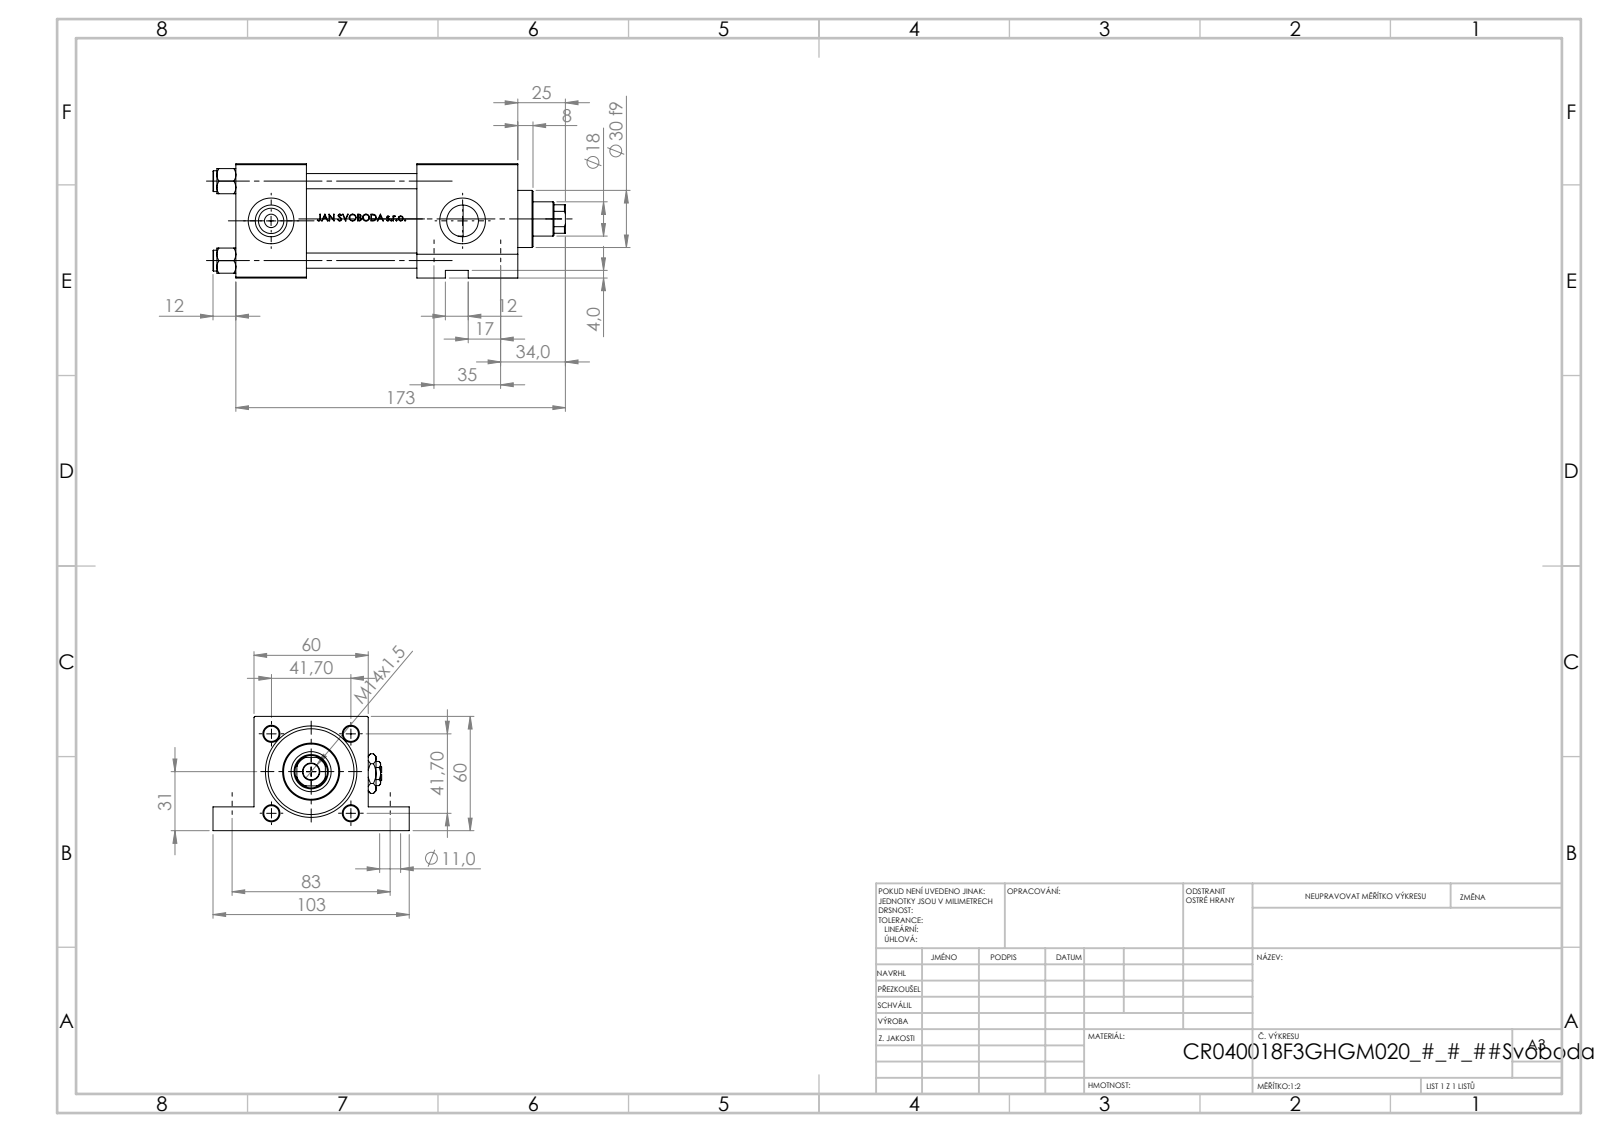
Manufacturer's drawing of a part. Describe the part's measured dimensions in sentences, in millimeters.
The part is named "V215CR_VCP_F; V215CR_F_TYCINKA; V215CR_F_Body; Zatka_pro_OIL_PORT (+2 more)". Its 3-D file was written by "SolidWorks 2019 (CONFIG_CONTROL_DESIGN)". It is 13 solids with 1215 faces: 484 planar, 149 cylindrical and 582 other. Overall it measures 185 by 103 by 60 millimeters. Its volume is 420 147 cubic millimeters and its surface area 114 523 square millimeters. Round holes: 4 of diameter 8, 3 of diameter 16.66, 3 of diameter 24, 2 of diameter 7, 2 of diameter 11, 2 of diameter 11, 1 of diameter 8.5, 1 of diameter 16, 1 of diameter 18, 1 of diameter 21, 1 of diameter 31, 1 of diameter 40. Round bosses or shafts: 4 of diameter 11, 1 of diameter 46, 1 of diameter 30. Partial cylindrical surfaces (rounded edges, fillets, slot ends): 1 of radius 8.5. The main face-to-face distances are 60, 37, 148, 111, 53, 58, 95, 119.3, 82.3, 24.3. The hole center spacings are 41.7, 28.79, 30.2, 35, 58.97, 83, 90.08, 8.
